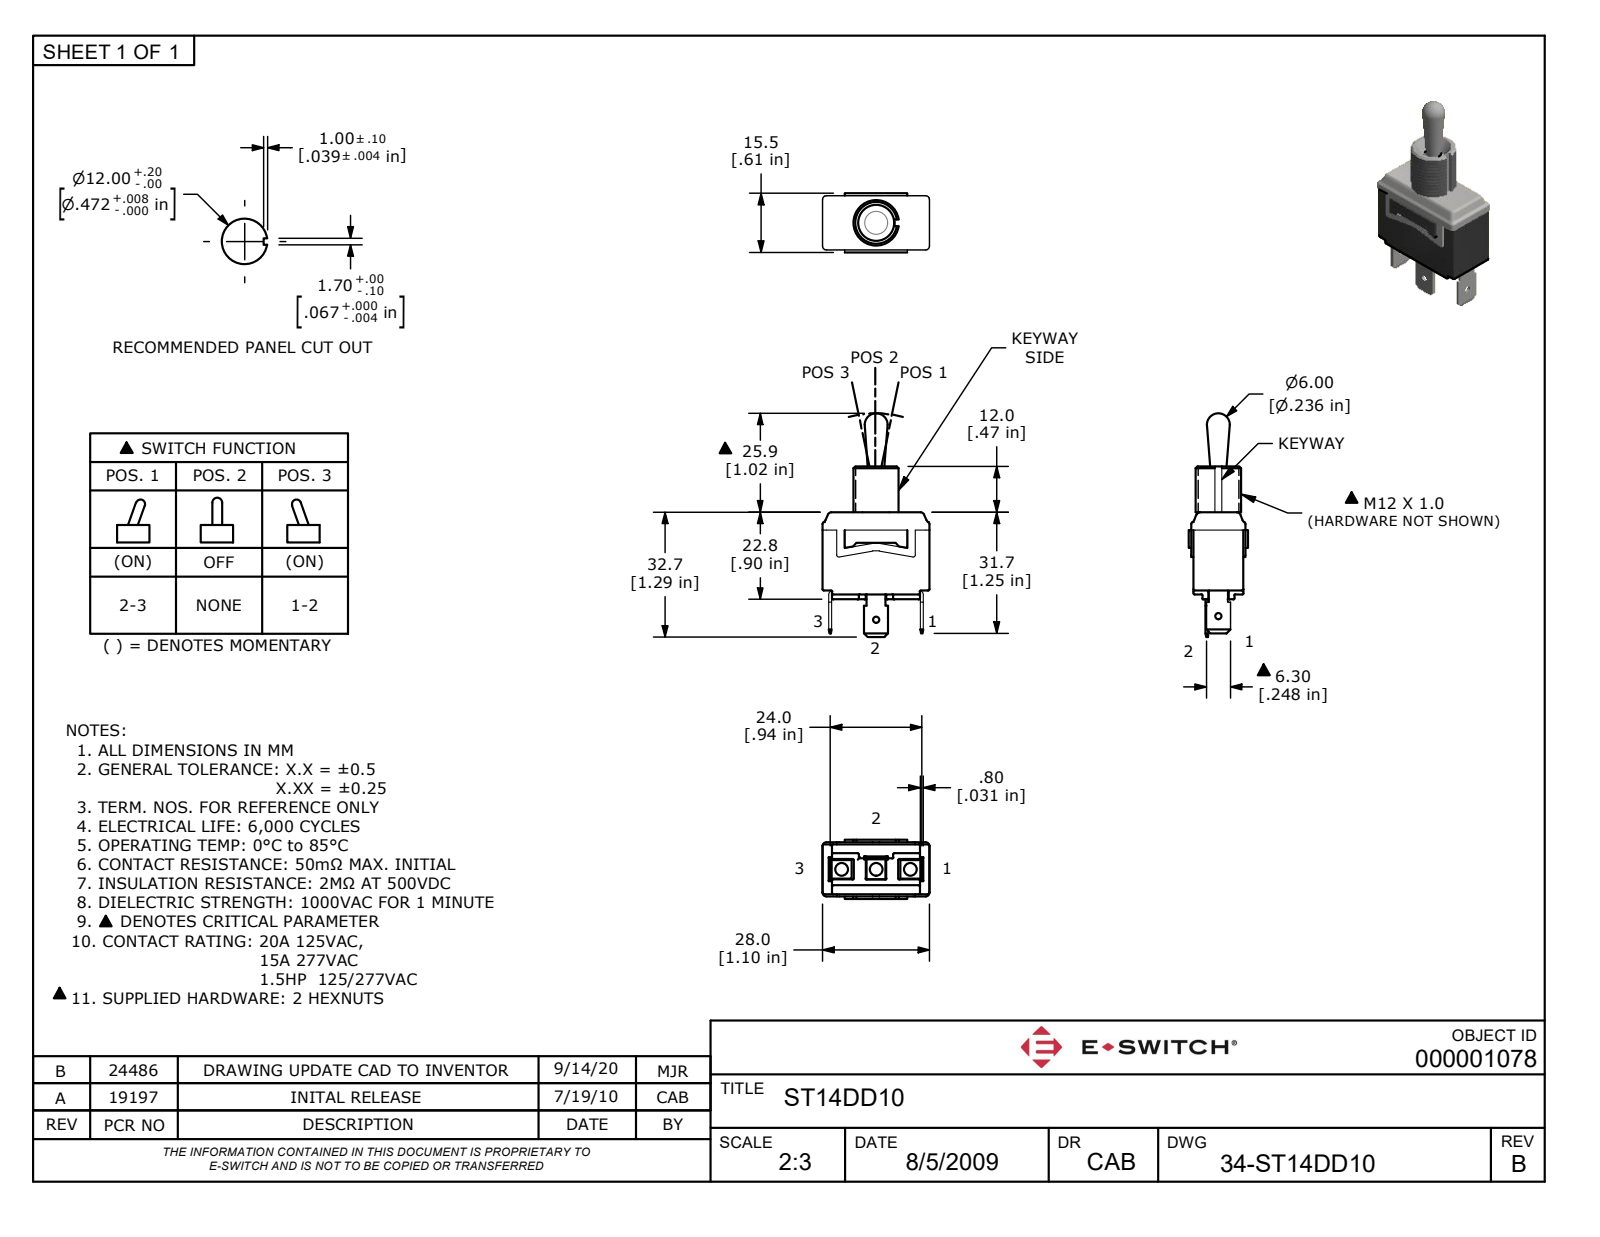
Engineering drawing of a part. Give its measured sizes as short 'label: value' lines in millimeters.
name: ST14DD10
written by: Autodesk Inventor 2022 (AUTOMOTIVE_DESIGN)
unit: mm
bodies: 1 solid, 411 faces (166 planar, 125 cylindrical, 120 other)
size: 58.6 × 28 × 15.5
volume: 9 607 mm³; area: 4 096 mm²
holes: 3× ⌀2, 2× ⌀1.7, 1× ⌀5.4
bosses: 1× ⌀11.91
rounds: 61× R0.3, 12× R1, 10× R0.5, 4× R0.6, 4× R0.8, 3× R1.1
face distances: 13.1, 0.55, 0.8, 13.65, 27.94, 14.85, 1.2, 0.65, 14.3, 1.57
hole spacings: 9, 18
